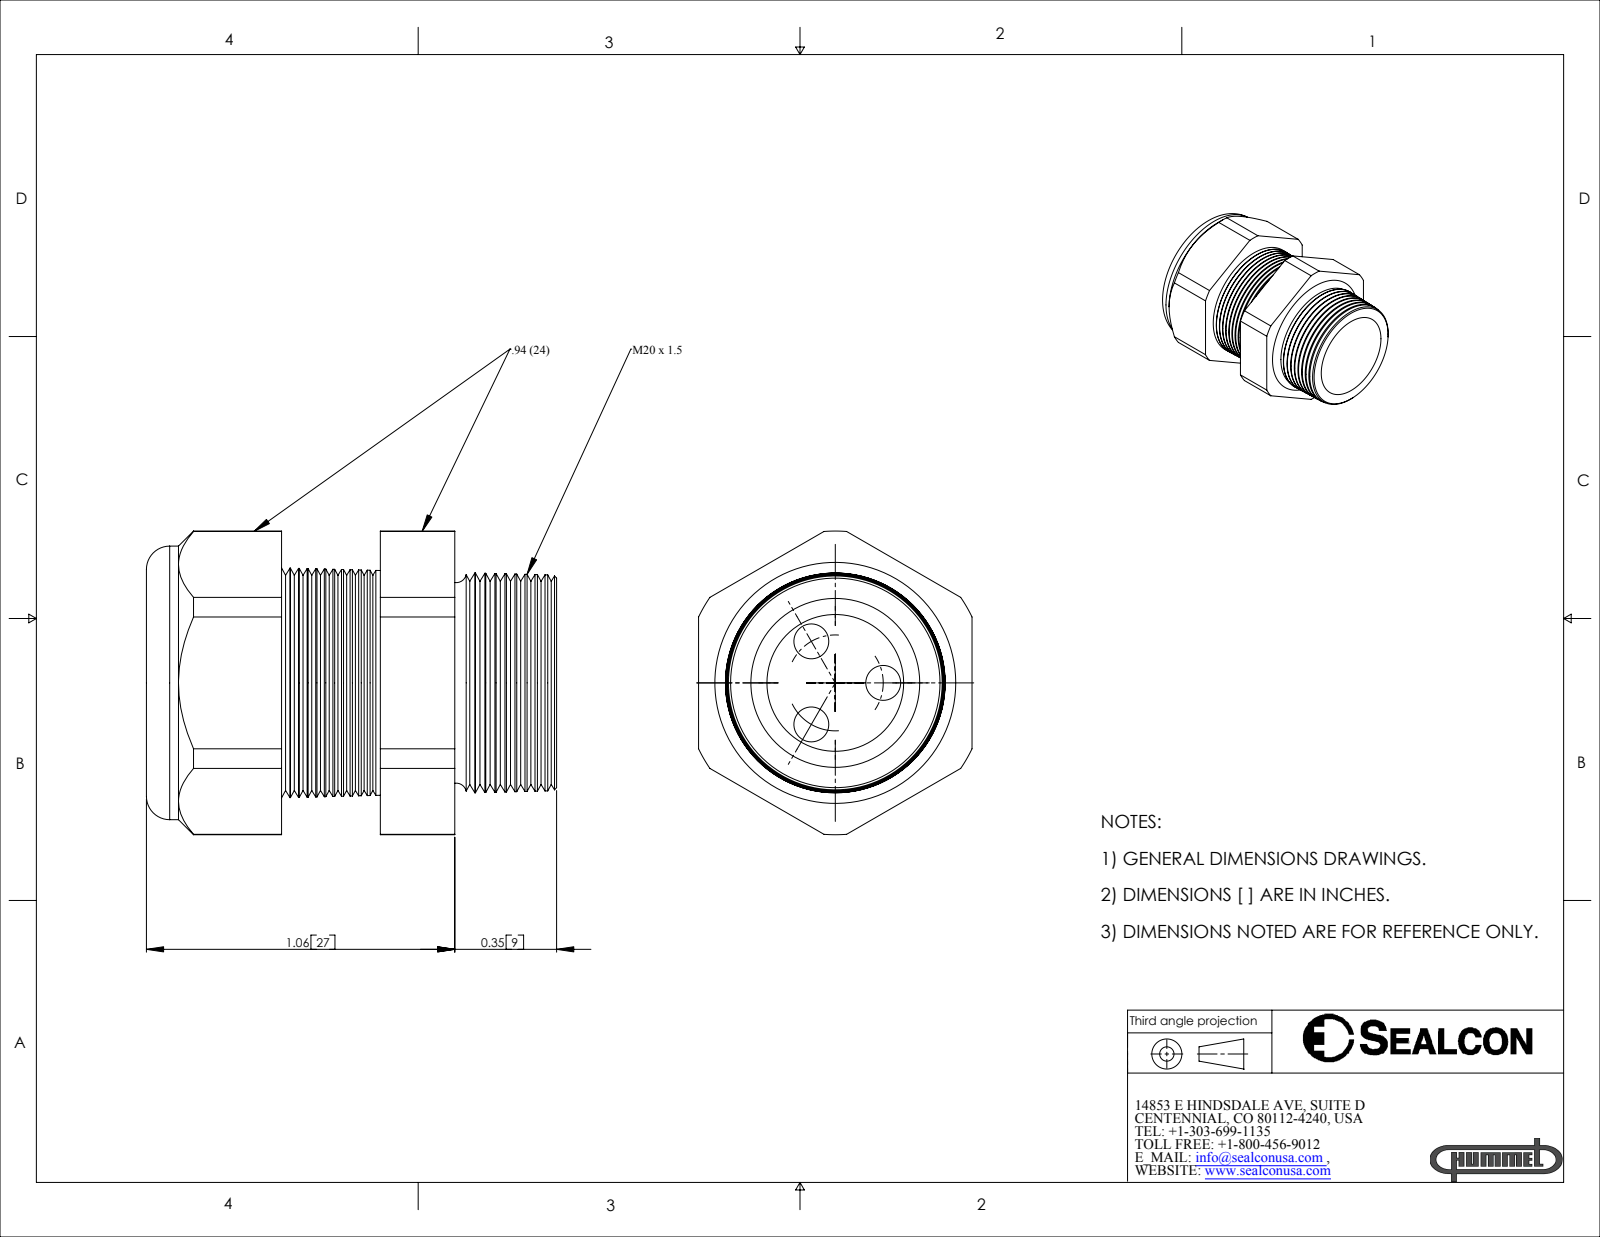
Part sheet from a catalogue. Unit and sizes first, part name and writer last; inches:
Units: inches
Overall size (bounding box): 1.41 × 1.043 × 0.94
Round holes (diameter × count): ⌀0.12 ×3, ⌀0.45 ×1, ⌀0.47 ×1
Round bosses / shafts (diameter × count): ⌀0.94 ×1
Partial cylindrical surfaces — rounded edges, fillets, slot ends (radius × count): R0.522 ×1
Main face-to-face distances: 0.94, 0.804, 0.465, 0.34, 1.06, 0.596, 0.256, 1.41, 0.946, 0.606
Hole centre spacings: 0.165, 0.285
Volume: 0.578 in³ · Surface area: 9.933 in²
Bodies: 2 solids, 180 faces (20 planar, 26 cylindrical, 134 other)
Part name (STEP PRODUCT): CD20M5-BK
STEP written by: SolidWorks 2007 (CONFIG_CONTROL_DESIGN)
